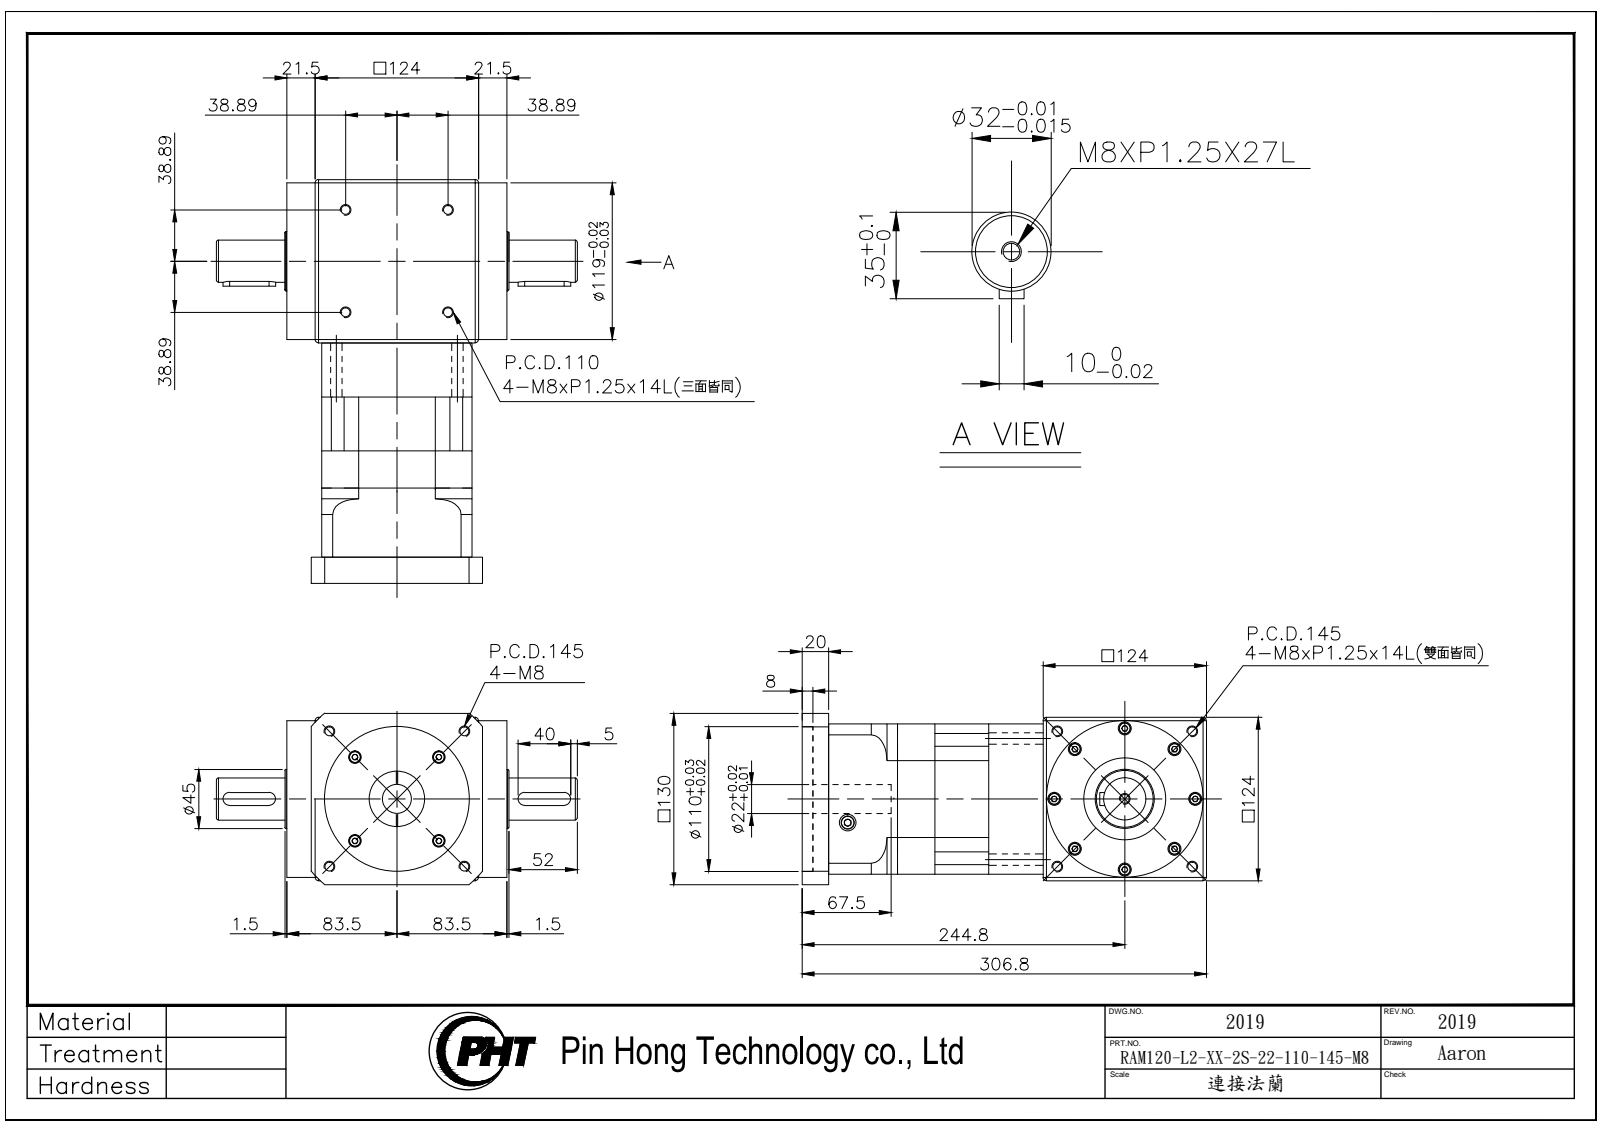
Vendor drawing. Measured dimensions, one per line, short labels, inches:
name: RAM120-L2-XX-2S-22-110-145-M8_2019
written by: SolidWorks 2016 (AUTOMOTIVE_DESIGN)
unit: in
bodies: 7 solids, 900 faces (424 planar, 312 cylindrical, 164 other)
size: 12.079 × 10.787 × 5.118
volume: 279.7 in³; area: 600.2 in²
holes: 17× ⌀0.268, 12× ⌀0.374, 8× ⌀0.209, 8× ⌀0.354, 8× ⌀0.551, 4× ⌀0.165, 4× ⌀0.217, 4× ⌀0.339, 2× ⌀0.5, 1× ⌀0.161, 1× ⌀0.866, 1× ⌀1.654
bosses: 12× ⌀0.512, 4× ⌀0.335, 1× ⌀4.685, 1× ⌀2.441, 1× ⌀1.929, 1× ⌀1.772, 1× ⌀1.26
rounds: 4× R0.197, 4× R0.276, 1× R2.52, 1× R2.953, 1× R3.346, 1× R3.394
face distances: 0.197, 4.685, 4.882, 4.488, 2.736, 1.114, 1.622, 0.118, 1.614, 4.35
hole spacings: 2.323, 0.394, 0.606, 0.679, 0.765, 0.857, 1.567, 2.019
